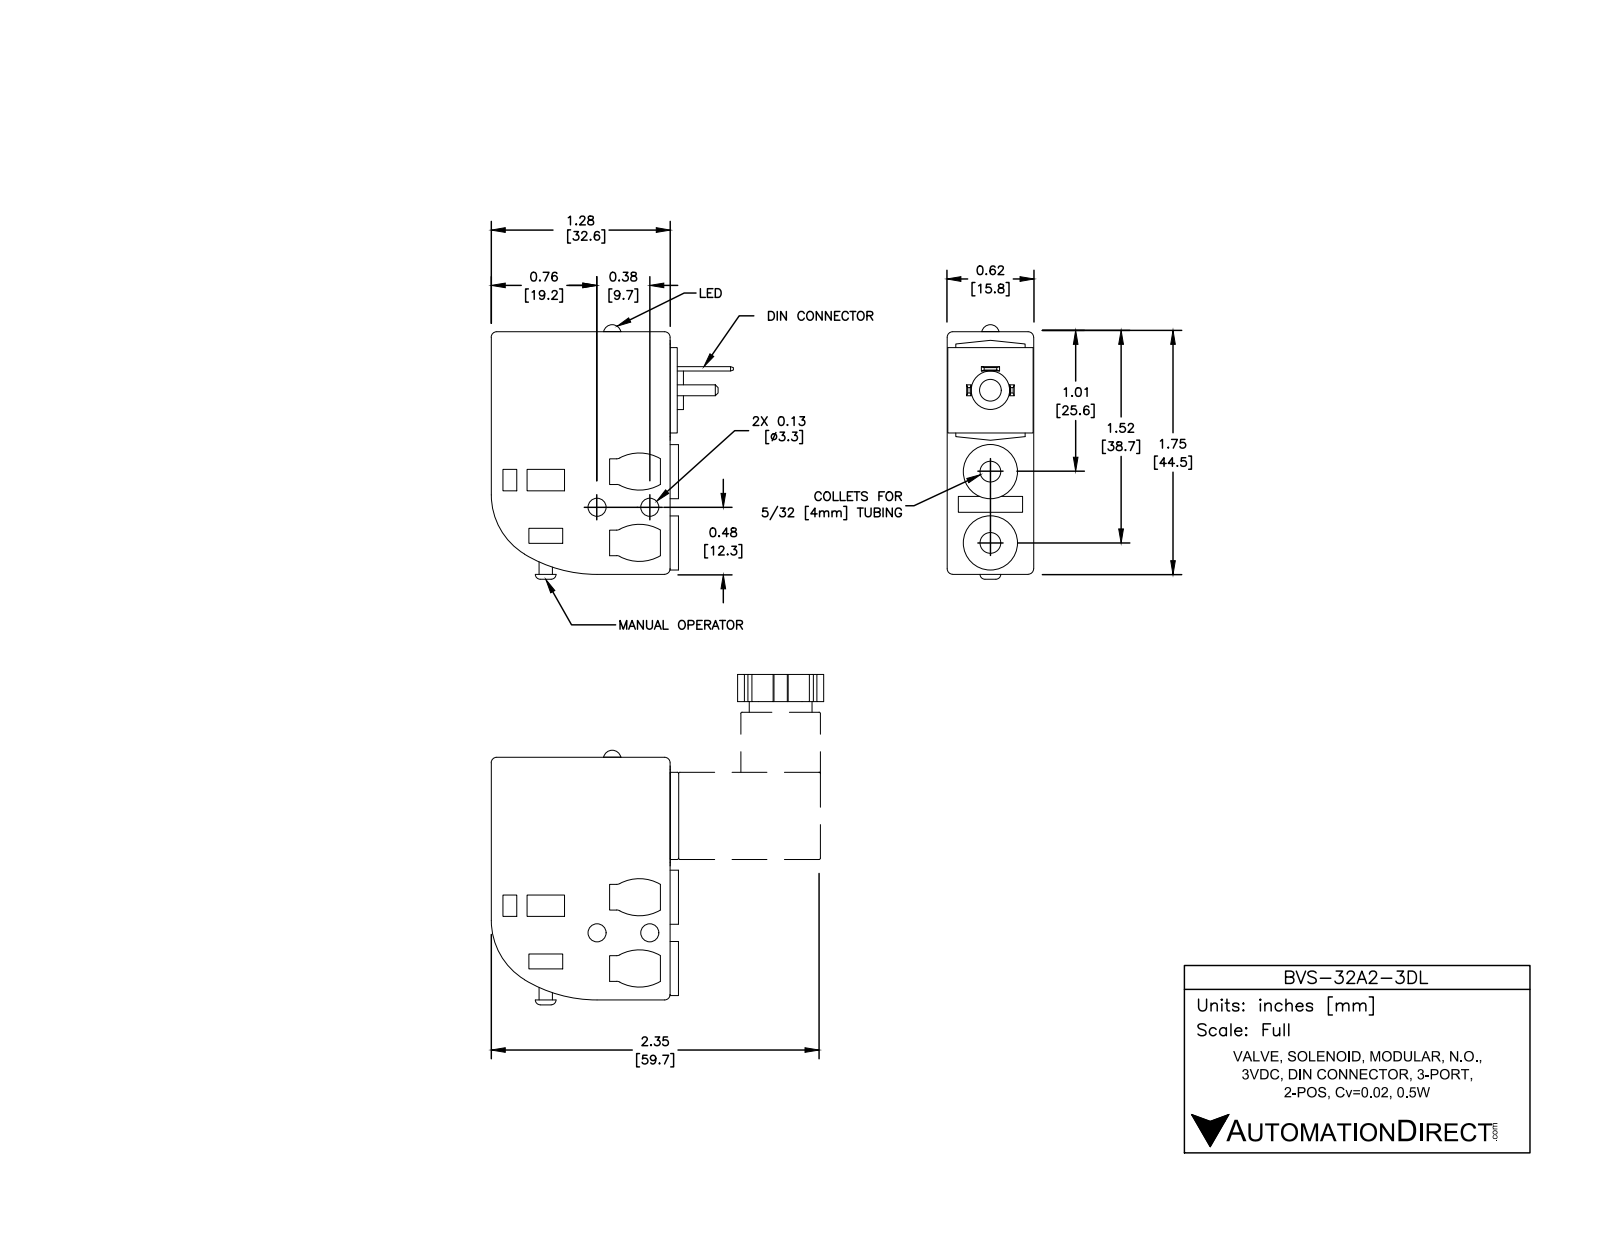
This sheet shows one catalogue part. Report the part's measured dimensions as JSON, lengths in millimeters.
{"part_name": "BVS-32A2-3DL", "step_written_by": "SolidWorks 2016 (AUTOMOTIVE_DESIGN)", "units": "millimeters", "bodies": {"solids": 1, "faces": 162, "planar": 112, "cylindrical": 46, "other": 4}, "overall_size": [46.7, 44.5, 15.7], "volume_mm3": 20960, "surface_area_mm2": 6935, "round_holes": [[3.3, 2], [3.8, 2], [6.4, 2], [1.3, 1], [4.1, 1]], "round_bosses_or_shafts": [[9.9, 2], [7.1, 1], [2.5, 1]], "partial_cylinders_radius": [[1.3, 4], [7.6, 4], [1, 3], [12.7, 1], [25.4, 1]], "face_to_face_distances": [15.7, 2.5, 32.8, 13.2, 34.1, 1.3, 44.5, 25.4, 3.8, 1.5], "hole_center_spacings": [1.5, 9.7, 11.4, 13, 15, 16.5, 27.9]}
